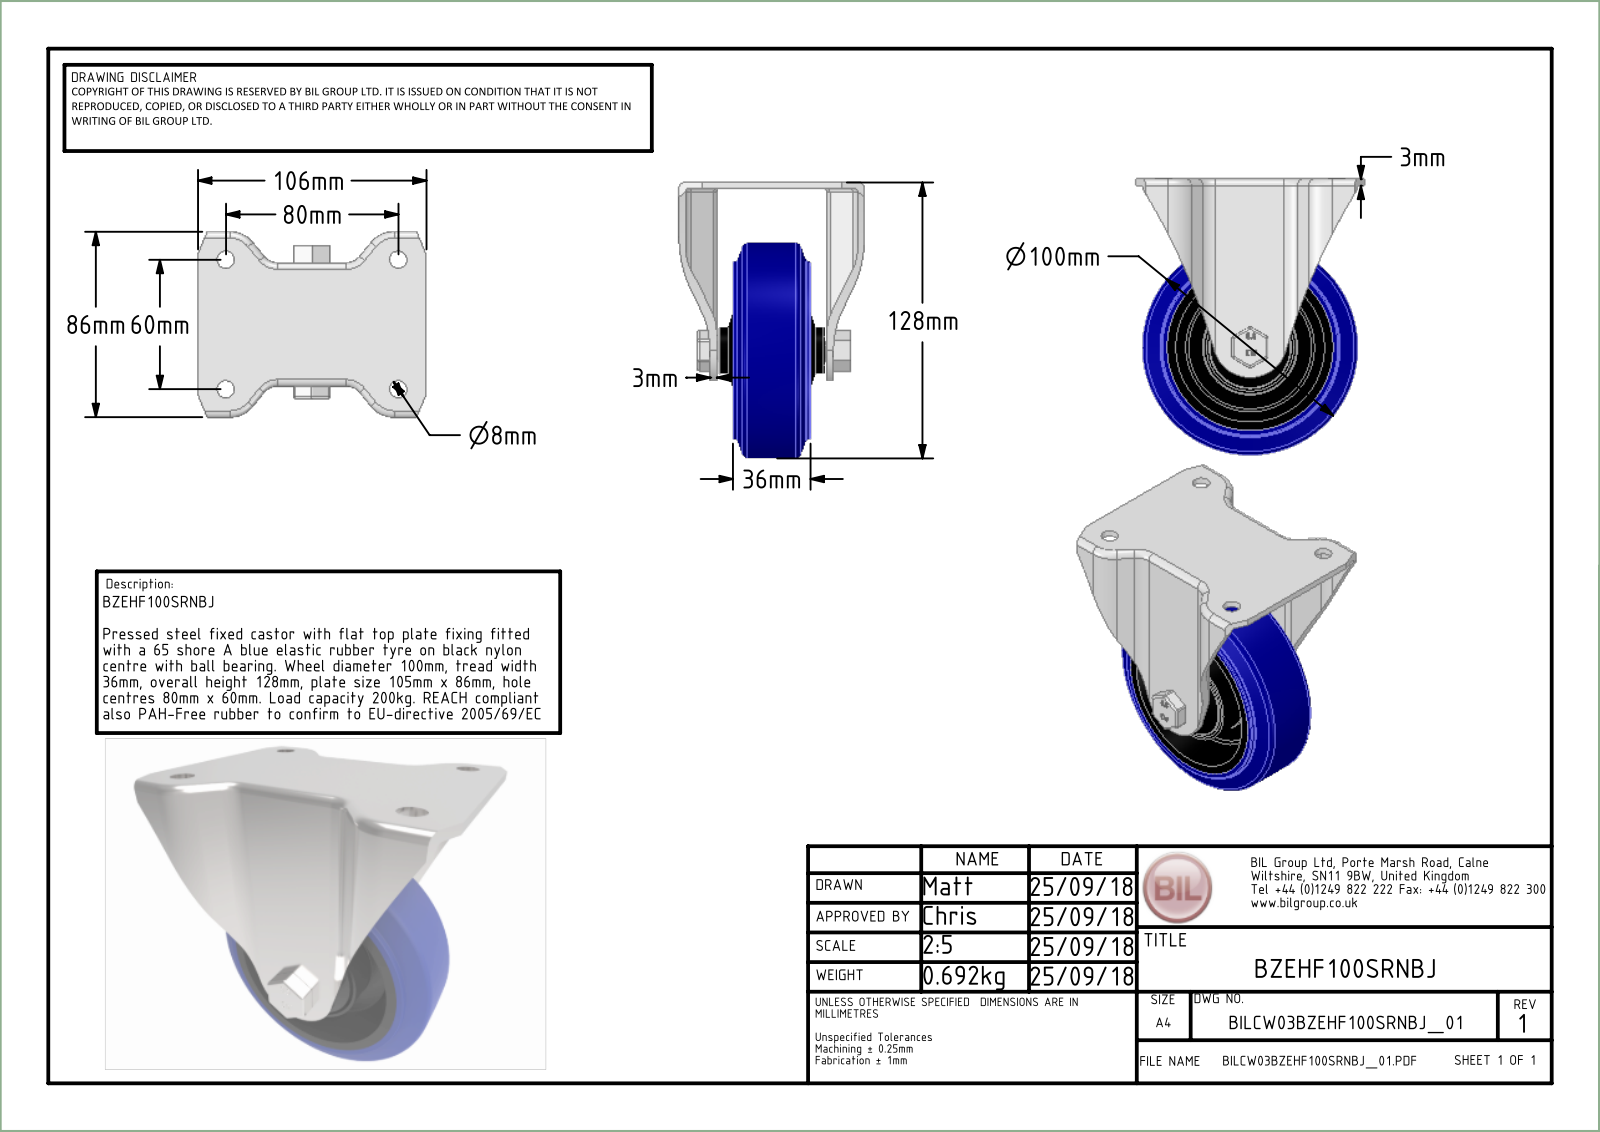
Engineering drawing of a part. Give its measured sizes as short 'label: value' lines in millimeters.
name: BZEHF100SRNBJ v3; BZHF100AS v1; ZINC PLATED, PRESSED STEEL BRACKET; BZH100WSRNBJM10 v1 (+7 more)
written by: Autodesk Translation Framework v13.20.0.188 (AUTOMOTIVE_DESIGN)
unit: mm
bodies: 21 solids, 747 faces (284 planar, 191 cylindrical, 272 other)
size: 128 × 106 × 88
volume: 244 500 mm³; area: 118 239 mm²
holes: 1× ⌀10, 1× ⌀10.2, 1× ⌀10.25, 1× ⌀12, 1× ⌀15, 1× ⌀20, 1× ⌀22.5, 1× ⌀26, 1× ⌀30, 1× ⌀31, 1× ⌀32, 1× ⌀33
bosses: 1× ⌀80, 1× ⌀43, 1× ⌀38.5, 1× ⌀35, 1× ⌀30.5, 1× ⌀28, 1× ⌀23, 1× ⌀22
rounds: 18× R0.5, 12× R1.5, 10× R3, 8× R4.5, 6× R0.75, 5× R12, 4× R6, 4× R8
face distances: 3, 54, 3.01, 25.27, 10.5, 25.5, 43.5, 46.5, 7.5, 22.5
